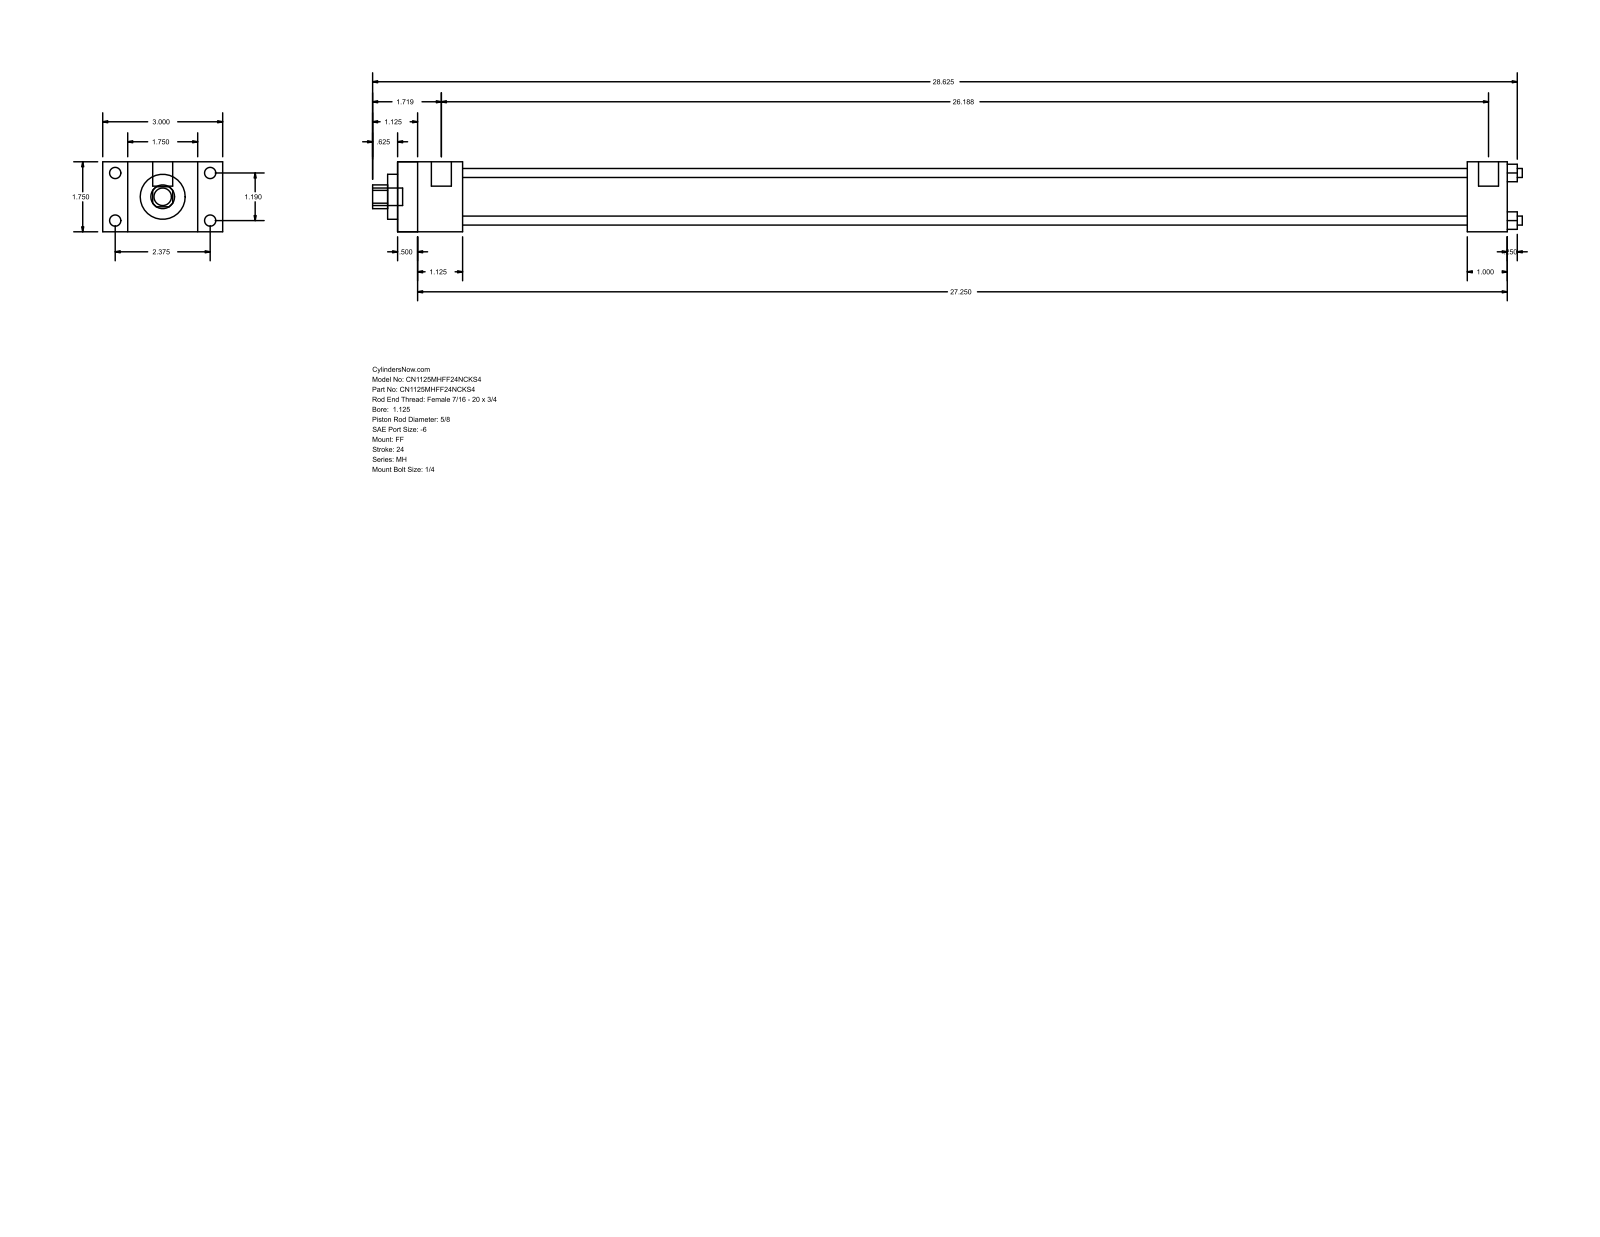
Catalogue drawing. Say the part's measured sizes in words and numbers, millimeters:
The part is named "MH_FF__0112_0.625". Its 3-D file was written by "GSSL Pune (CONFIG_CONTROL_DESIGN)". It is 0 solids with 92 faces: 64 planar, 28 cylindrical and 0 other. Overall it measures 730.25 by 76.2 by 44.45 millimeters. Round holes: 4 of diameter 5.71, 1 of diameter 15.88, 1 of diameter 28.57, 1 of diameter 34.92. Round bosses or shafts: 4 of diameter 7.14, 4 of diameter 5.56, 2 of diameter 12.7, 1 of diameter 11.11. Partial cylindrical surfaces (rounded edges, fillets, slot ends): 1 of radius 7.54. The main face-to-face distances are 44.46, 704.85, 15.87, 12.69, 692.16, 60.33, 28.58, 41.27, 679.45, 666.76. The hole center spacings are 21.37, 30.22, 42.74.
